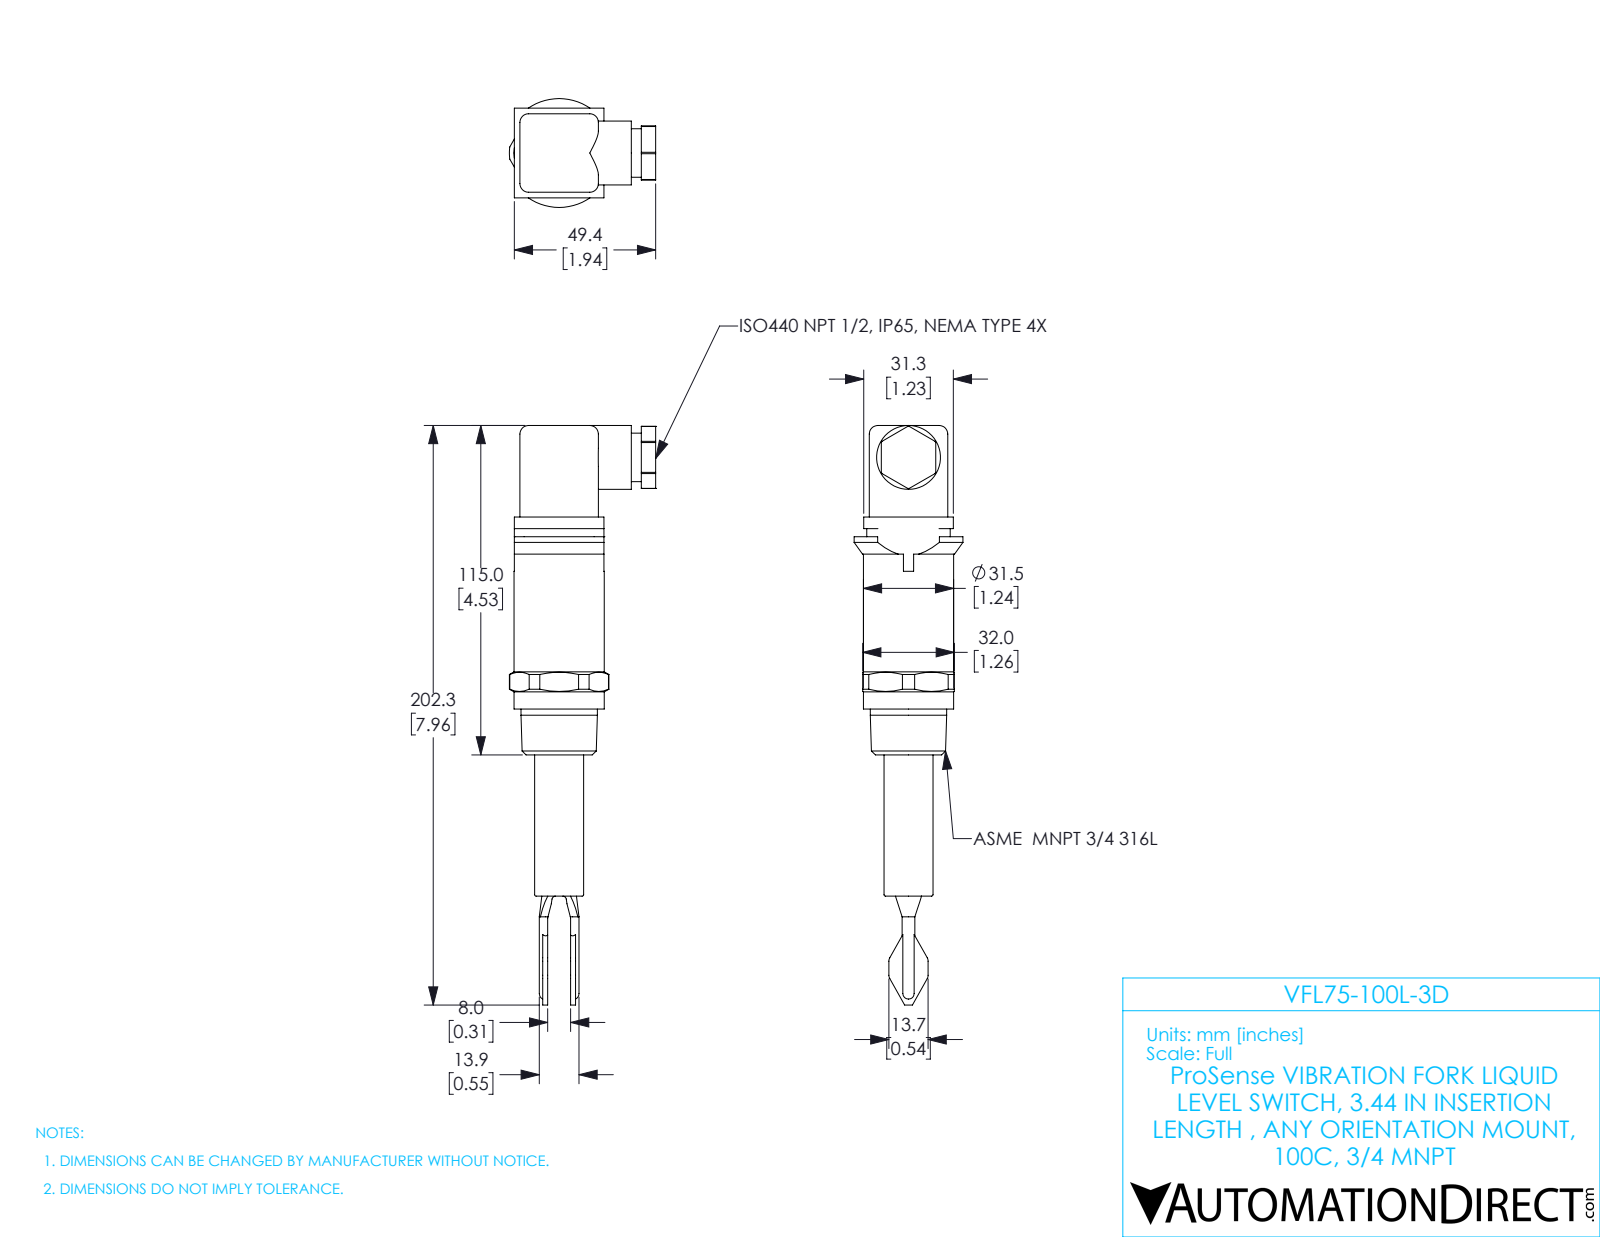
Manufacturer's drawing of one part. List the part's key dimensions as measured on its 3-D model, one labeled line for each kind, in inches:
Part name (STEP PRODUCT): VFL75-100L-3D
STEP written by: SolidWorks 2017 (AUTOMOTIVE_DESIGN)
Units: inches
Bodies: 1 solid, 155 faces (78 planar, 56 cylindrical, 21 other)
Overall size (bounding box): 7.965 × 2.011 × 1.496
Volume: 6.521 in³ · Surface area: 29.85 in²
Round bosses / shafts (diameter × count): ⌀1.24 ×1, ⌀1.05 ×1, ⌀0.878 ×1, ⌀0.673 ×1, ⌀0.667 ×1
Partial cylindrical surfaces — rounded edges, fillets, slot ends (radius × count): R0.119 ×8, R0.047 ×4, R0.094 ×4, R0.154 ×4, R0.088 ×2, R0.426 ×1, R0.684 ×1, R0.748 ×1
Main face-to-face distances: 1.079, 0.077, 1.156, 0.459, 0.774, 0.382, 0.697, 1.232, 1.169, 1.943
